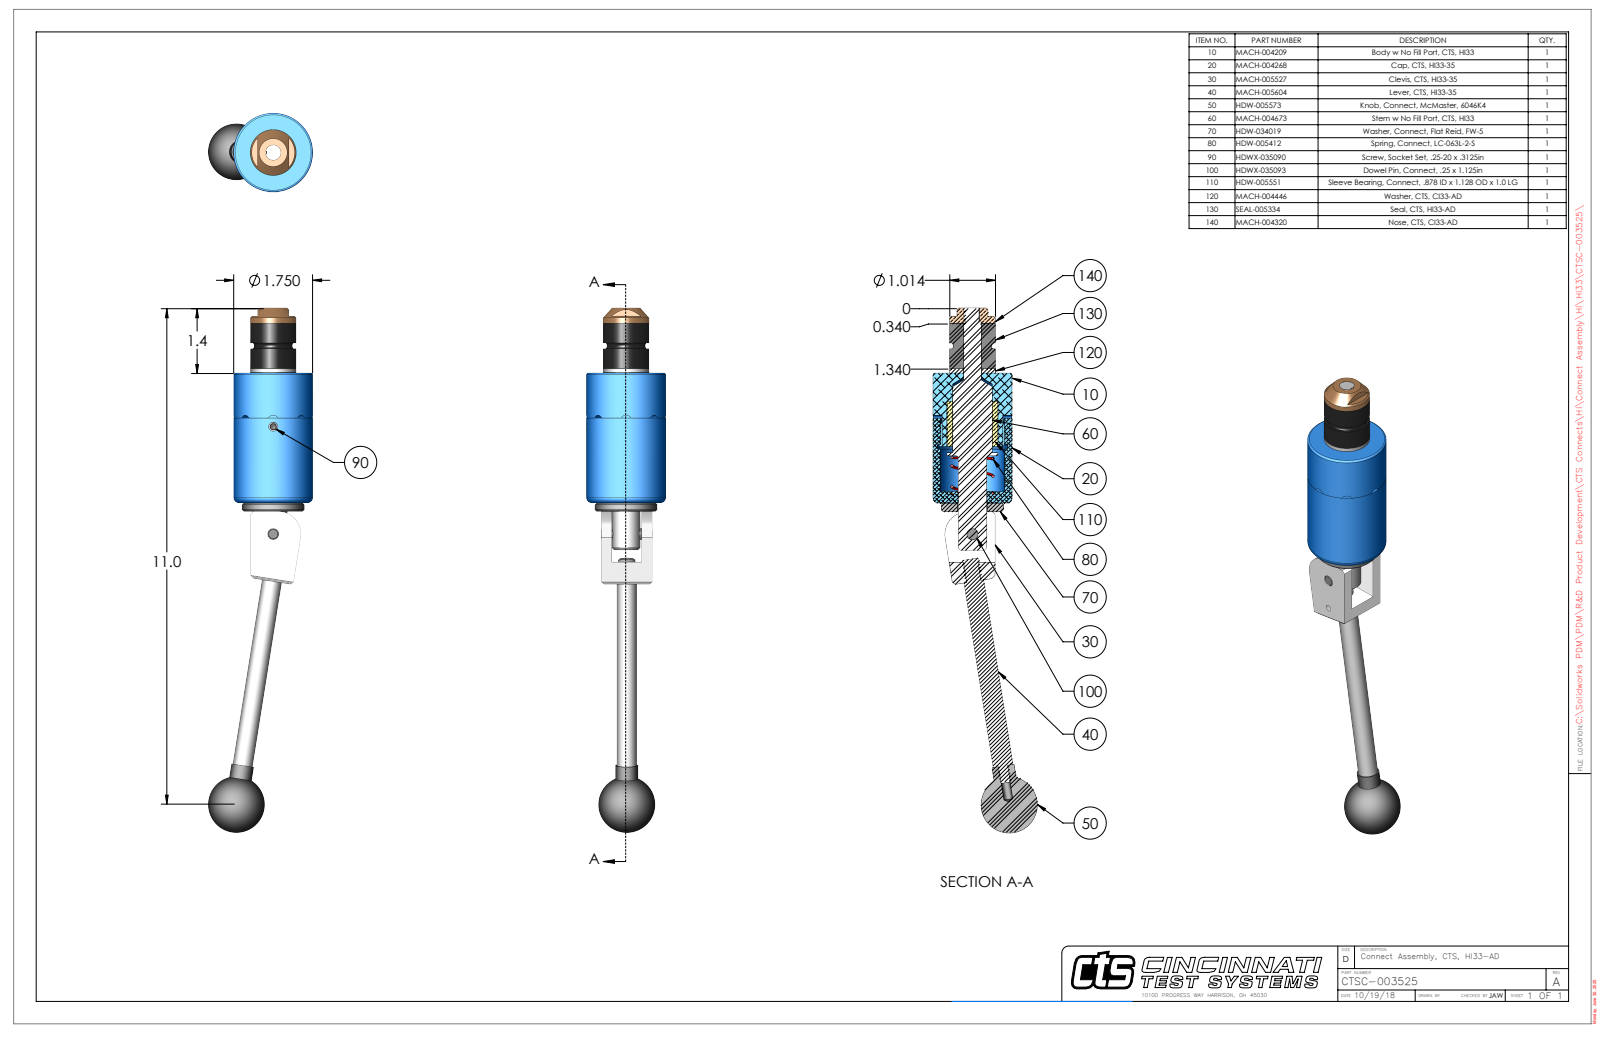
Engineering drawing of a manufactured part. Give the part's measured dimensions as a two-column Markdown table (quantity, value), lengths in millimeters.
| quantity | value |
| --- | --- |
| part name | CTSC-003525 |
| STEP written by | SolidWorks 2023 (AUTOMOTIVE_DESIGN) |
| units | millimeters |
| bodies | 9 solids, 232 faces (78 planar, 95 cylindrical, 59 other) |
| overall size | 295 × 58.7 × 44.5 |
| volume | 183 500 mm³ |
| surface area | 40 850 mm² |
| round holes (diameter × count) | 5.1 × 2, 8 × 2, 3.8 × 1, 6.3 × 1, 6.4 × 1, 9.9 × 1, 10.1 × 1, 10.2 × 1, 16.1 × 1, 16.7 × 1, 36 × 1 |
| round bosses / shafts (diameter × count) | 9.5 × 2, 7.9 × 2, 6.4 × 2, 44.5 × 1, 35.1 × 1, 25.8 × 1, 15.9 × 1, 12.7 × 1 |
| partial cylindrical surfaces (radius × count) | 3.2 × 4, 0.7 × 2, 12.7 × 1, 17.7 × 1, 21.2 × 1 |
| main face-to-face distances | 73.1, 27.9, 25.4, 28.4, 101, 2.5, 75.6, 105.8, 80.4, 77.9 |
| hole center spacings | 18.8, 60.4, 79.1 |
